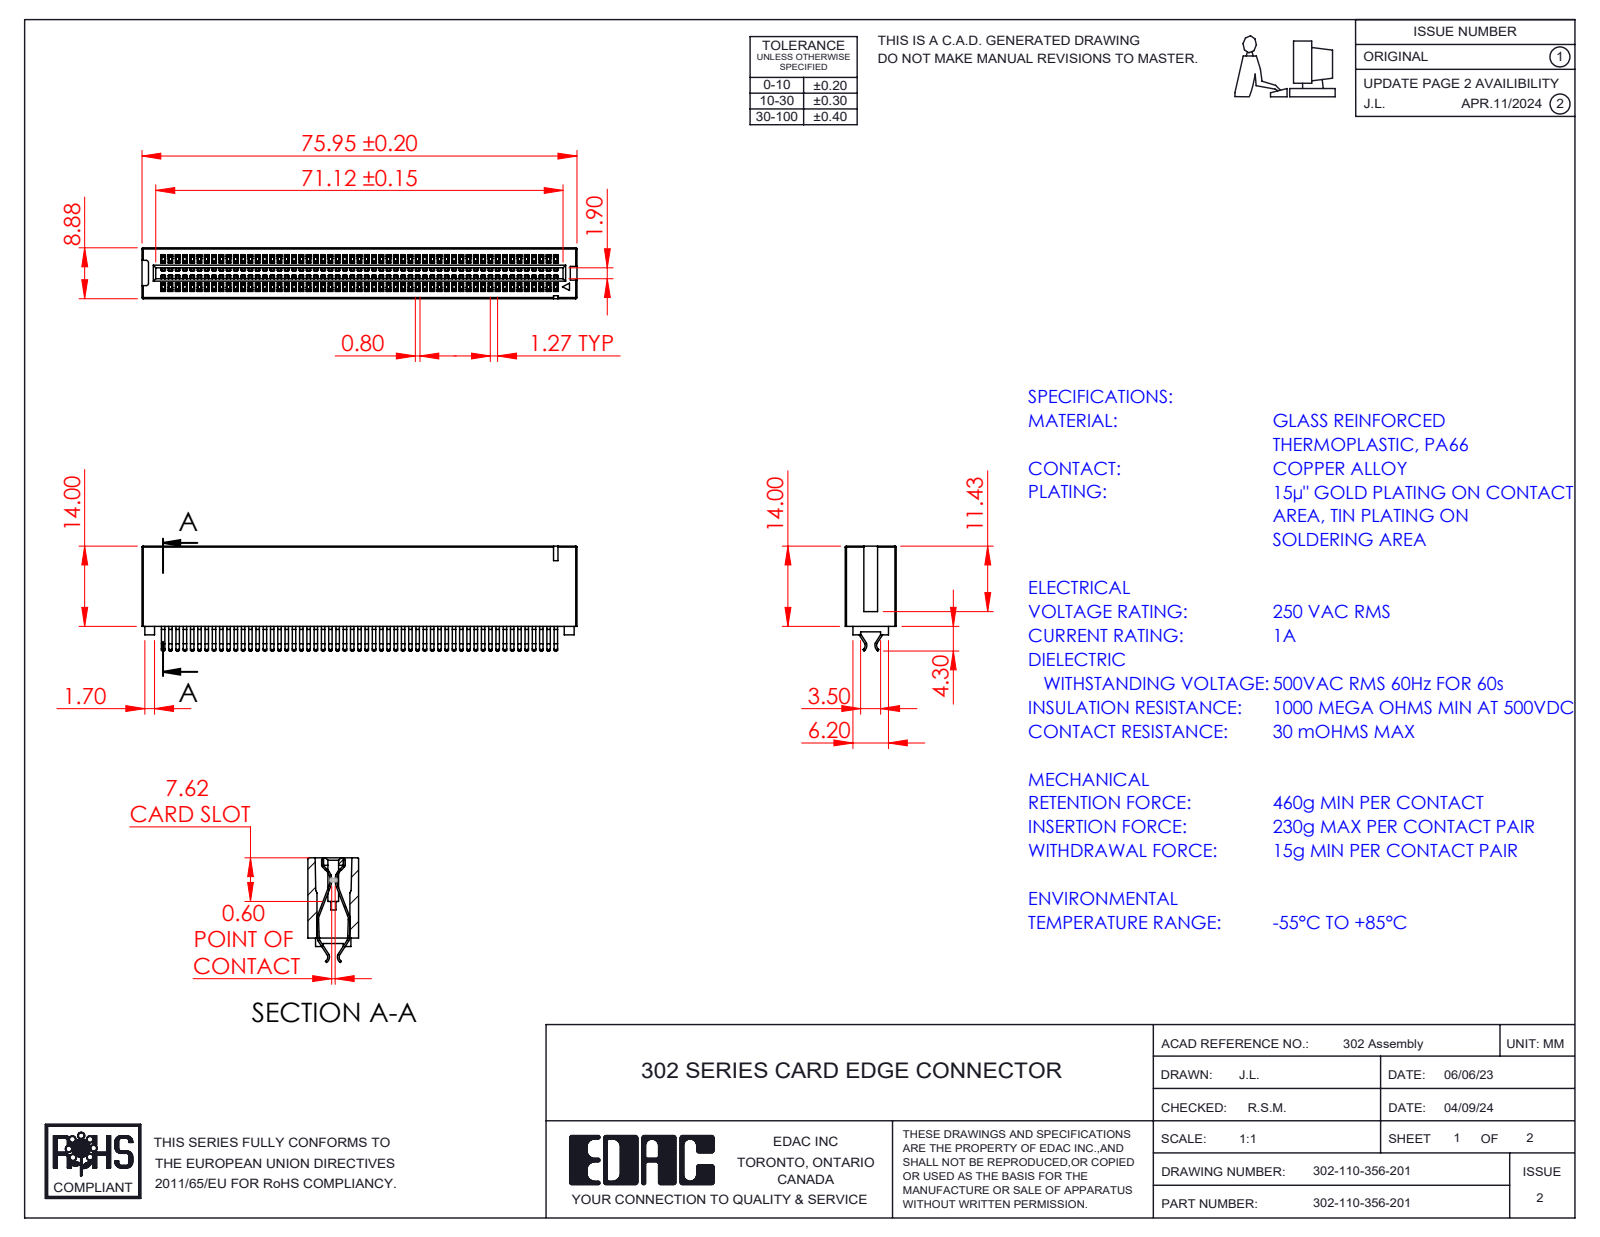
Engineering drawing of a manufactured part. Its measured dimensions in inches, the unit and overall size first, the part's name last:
Units: inches
Overall size (bounding box): 2.99 × 0.72 × 0.35
Partial cylindrical surfaces — rounded edges, fillets, slot ends (radius × count): R0.008 ×338, R0.004 ×2, R0.016 ×2, R0.016 ×2, R0.037 ×2, R0.041 ×2, R0.048 ×2, R0.049 ×2
Main face-to-face distances: 0.35, 0.05, 0.1, 0.15, 0.2, 0.3, 0.25, 0.35, 0.4, 0.075
Volume: 0.354 in³ · Surface area: 25.85 in²
Bodies: 111 solids, 5291 faces (3514 planar, 1773 cylindrical, 4 other)
Part name (STEP PRODUCT): Contact_302-290-X56; HSG_Vertical HSG; 302-110-356-201
STEP written by: SolidWorks 2023 (CONFIG_CONTROL_DESIGN)
